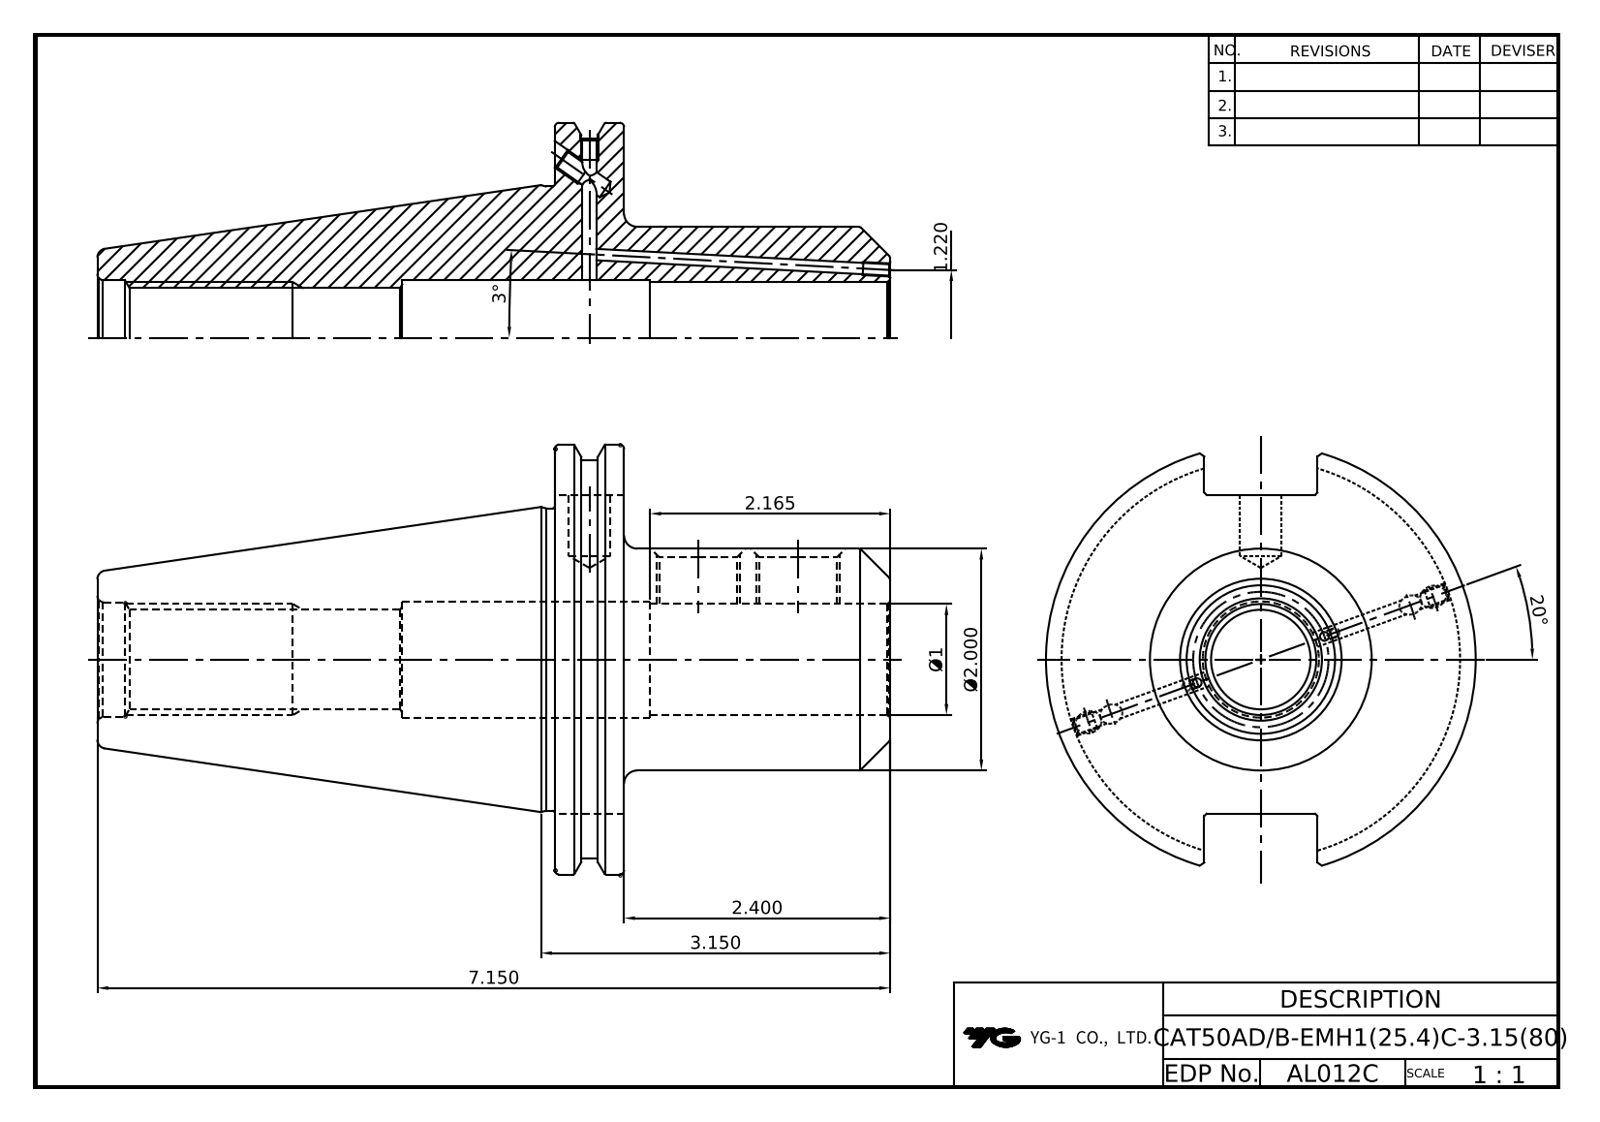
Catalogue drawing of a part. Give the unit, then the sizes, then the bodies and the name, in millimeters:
Units: millimetres
Overall size (bounding box): 181.6 × 98.42 × 94.69
Round holes (diameter × count): ⌀2.46 ×2, ⌀3.24 ×2, ⌀4.13 ×2, ⌀4.2 ×2, ⌀5 ×2, ⌀17.32 ×2, ⌀9.53 ×1, ⌀21.97 ×1, ⌀25.4 ×1, ⌀26.2 ×1, ⌀26.6 ×1
Round bosses / shafts (diameter × count): ⌀98.42 ×1, ⌀91.29 ×1, ⌀69.25 ×1, ⌀50.8 ×1
Main face-to-face distances: 15.88, 104.77, 120.65, 181.6, 76.83, 60.95, 73.03, 25.9, 114.64, 9.87
Hole centre spacings: 22.9, 24.87, 47.77
Volume: 390 230 mm³ · Surface area: 60 965 mm²
Bodies: 1 solid, 91 faces (39 planar, 29 cylindrical, 23 other)
Part name (STEP PRODUCT): LO-CAT50ADB-EMH25.4C-80
STEP written by: Autodesk Inventor 2025 (AUTOMOTIVE_DESIGN)
